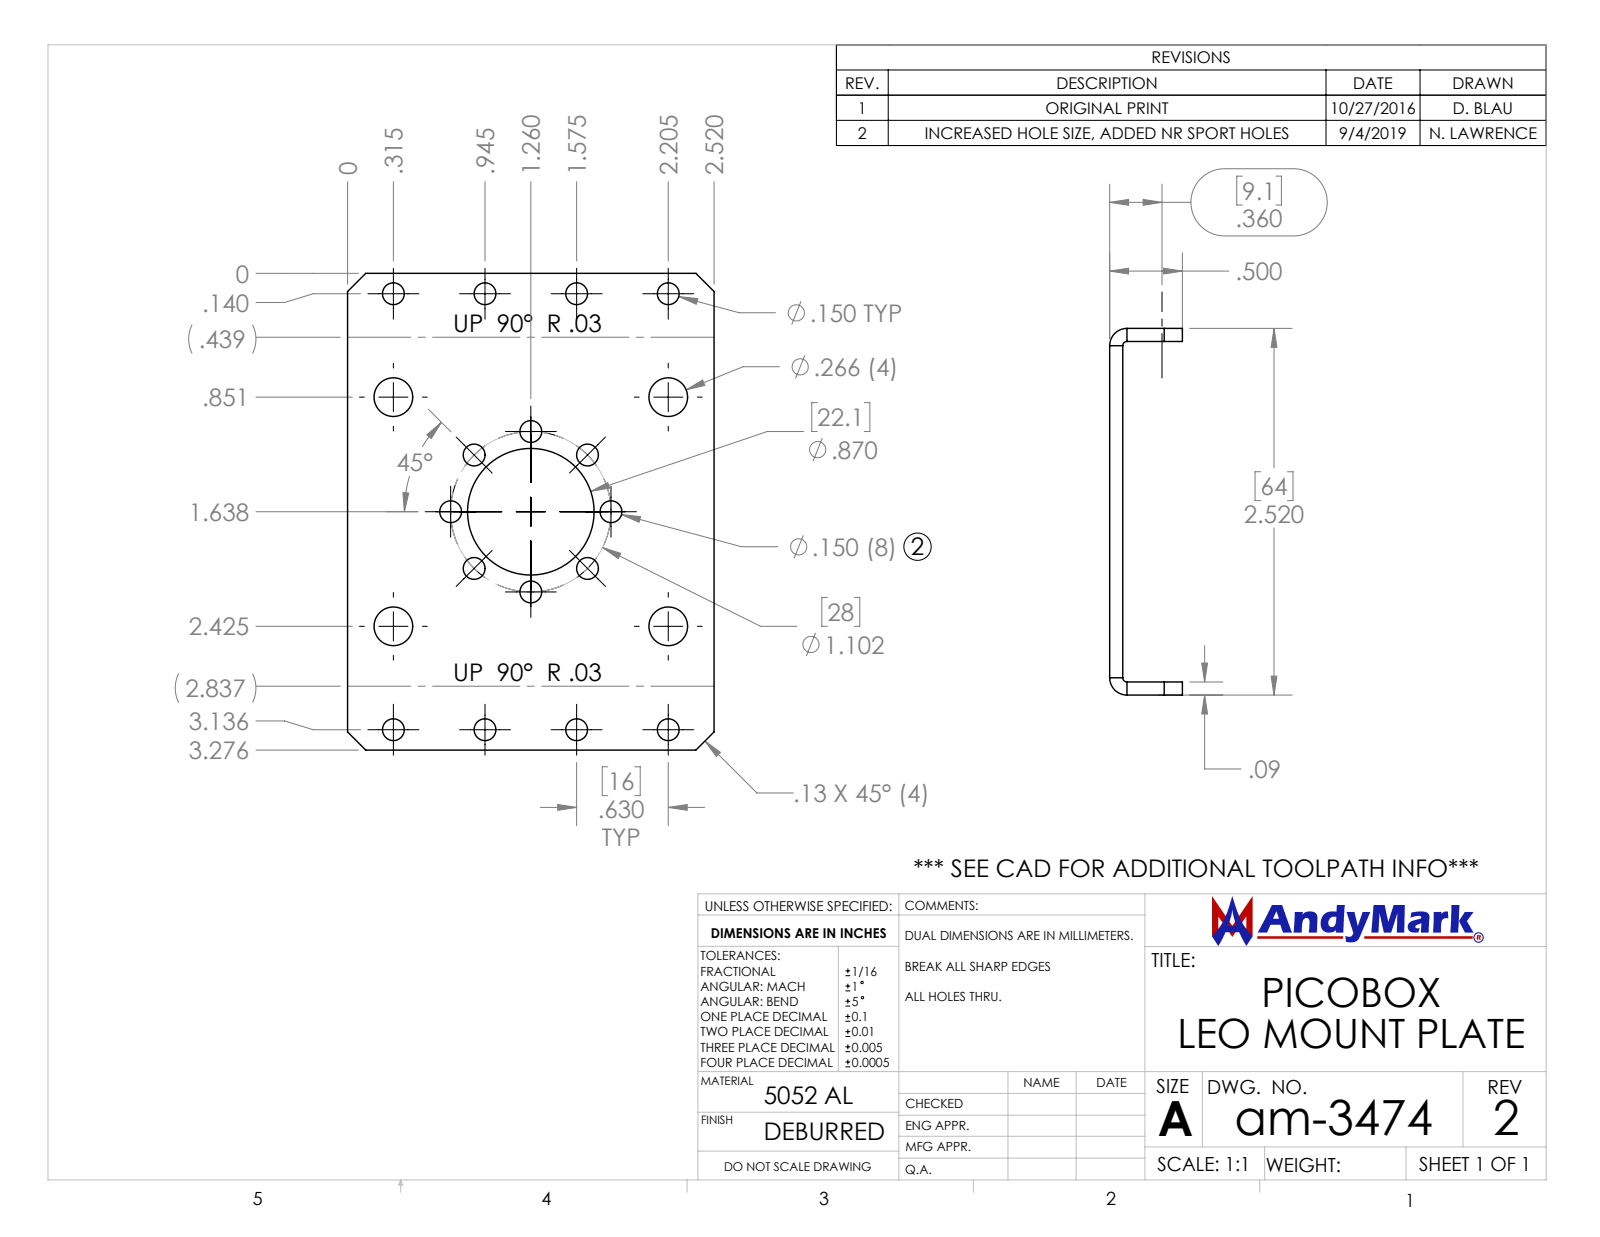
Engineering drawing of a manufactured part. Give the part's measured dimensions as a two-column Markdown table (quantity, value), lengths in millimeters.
| quantity | value |
| --- | --- |
| part name | am-3474 PicoBox LEO Mount Plate |
| STEP written by | SolidWorks 2019 (AUTOMOTIVE_DESIGN) |
| units | millimeters |
| bodies | 1 solid, 43 faces (22 planar, 21 cylindrical, 0 other) |
| overall size | 64 × 64 × 12.7 |
| volume | 10 600 mm³ |
| surface area | 10 620 mm² |
| round holes (diameter × count) | 3.8 × 8, 6.8 × 4, 22.1 × 1 |
| partial cylindrical surfaces (radius × count) | 0.7 × 2, 3 × 2 |
| main face-to-face distances | 2.3, 61.7, 64, 59.4, 12.7, 10.4 |
| hole center spacings | 14, 19.8, 22.4, 24.7, 31.2, 41.6, 43, 16 |
